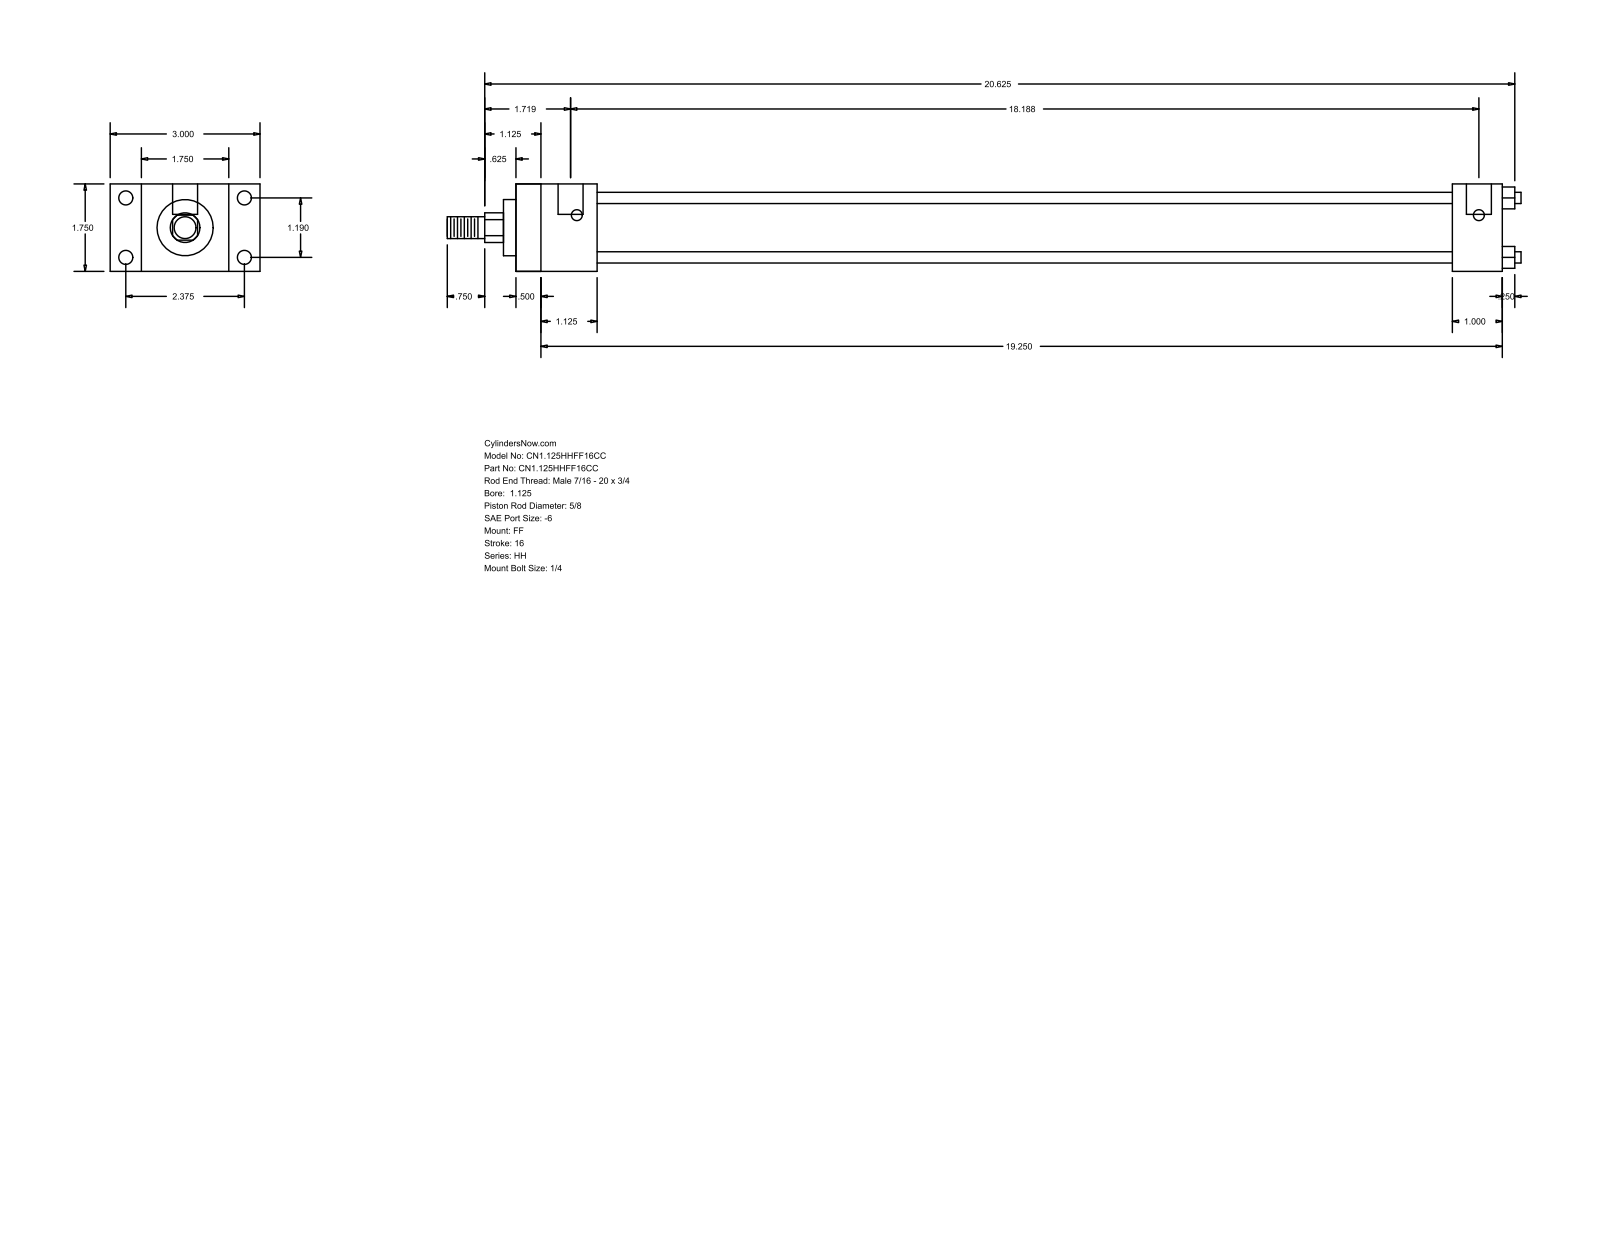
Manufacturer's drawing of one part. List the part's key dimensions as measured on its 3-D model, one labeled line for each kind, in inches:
Part name (STEP PRODUCT): HH_FF__0112_0.625
STEP written by: GSSL Pune (CONFIG_CONTROL_DESIGN)
Units: inches
Bodies: 0 solids, 92 faces (64 planar, 28 cylindrical, 0 other)
Overall size (bounding box): 21.5 × 3 × 1.75
Round holes (diameter × count): ⌀0.219 ×4, ⌀0.281 ×4, ⌀0.5 ×2
Round bosses / shafts (diameter × count): ⌀0.225 ×4, ⌀1.375 ×1, ⌀1.125 ×1, ⌀0.625 ×1, ⌀0.437 ×1
Partial cylindrical surfaces — rounded edges, fillets, slot ends (radius × count): R0.297 ×1
Main face-to-face distances: 1.75, 19.75, 0.5, 19.25, 0.625, 1.125, 2.375, 1, 1.625, 18.75
Hole centre spacings: 1.19, 2.375, 2.656, 18.063, 0.125, 18.187
